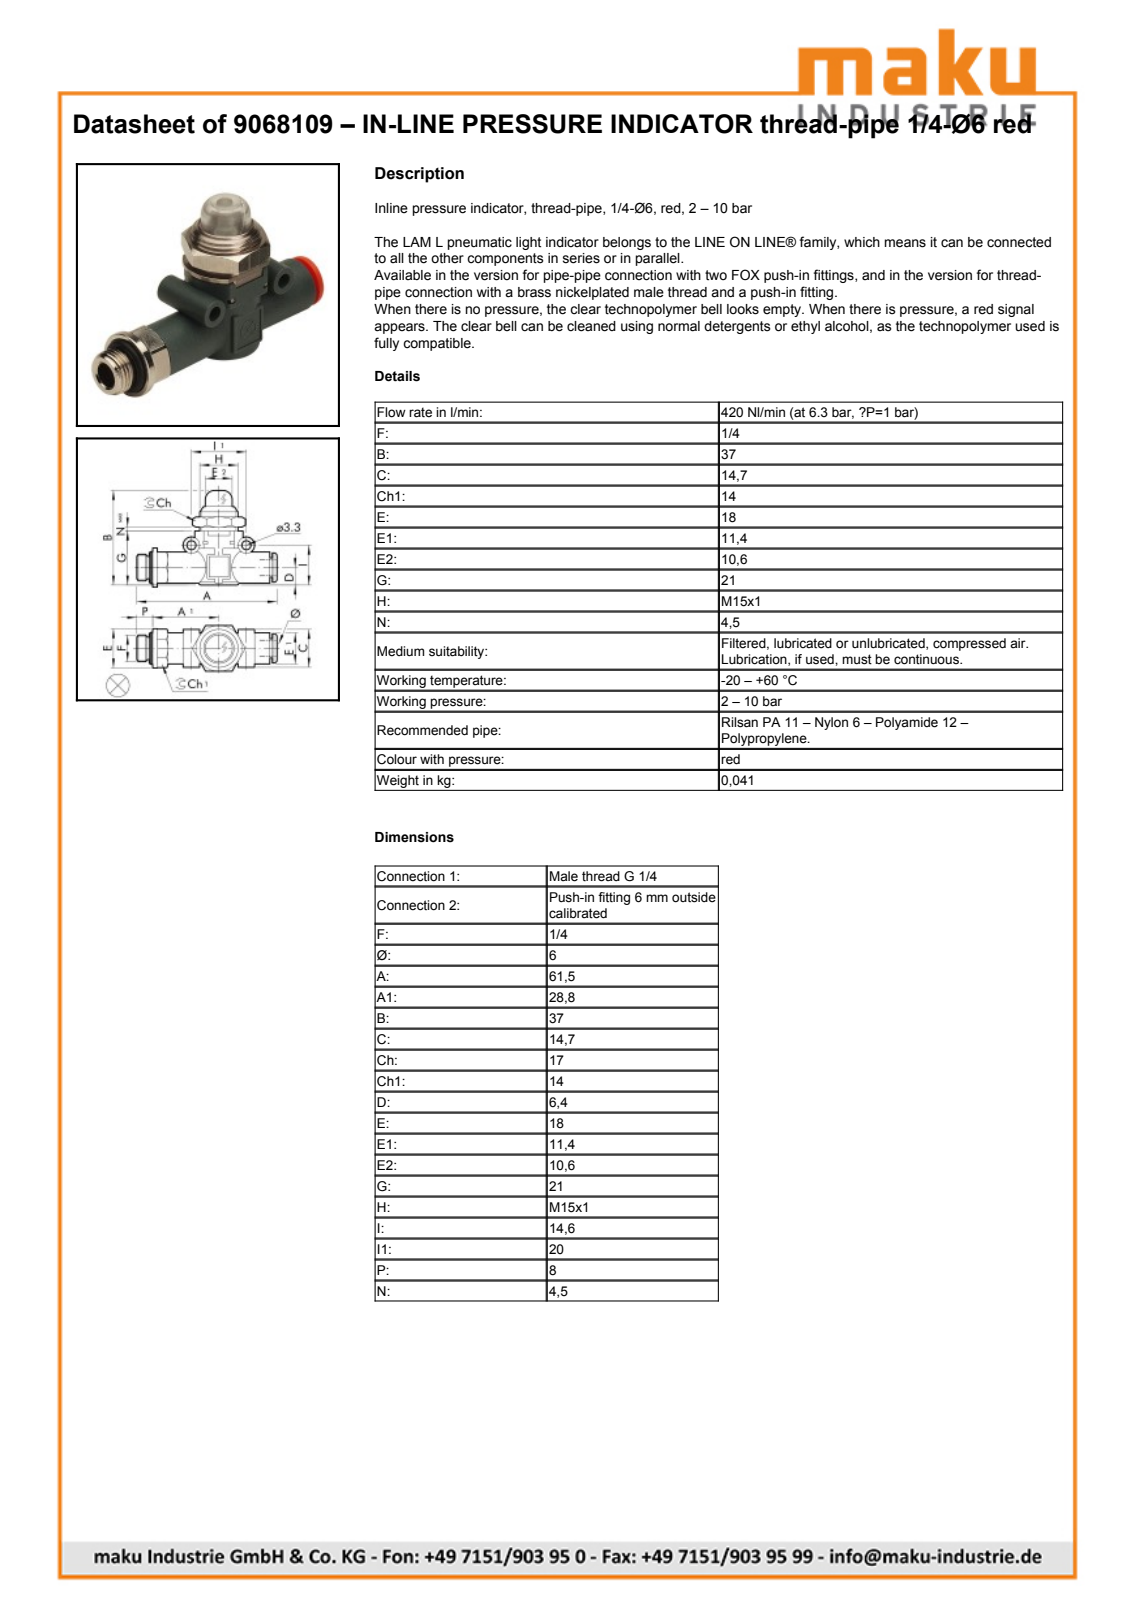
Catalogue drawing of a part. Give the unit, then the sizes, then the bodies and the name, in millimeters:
Units: millimetres
Overall size (bounding box): 61.5 × 39.6 × 18
Round holes (diameter × count): ⌀3.3 ×2, ⌀3.5 ×1, ⌀4 ×1, ⌀6 ×1, ⌀6.2 ×1, ⌀8 ×1, ⌀9 ×1, ⌀9.6 ×1, ⌀10.3 ×1, ⌀11.6 ×1
Round bosses / shafts (diameter × count): ⌀6 ×2, ⌀18 ×1, ⌀14.8 ×1, ⌀14 ×1, ⌀13.16 ×1, ⌀11.4 ×1, ⌀11.1 ×1, ⌀11 ×1
Partial cylindrical surfaces — rounded edges, fillets, slot ends (radius × count): R7.95 ×2, R3.75 ×1, R7.5 ×1, R7.9 ×1, R9.1 ×1, R9.15 ×1, R9.65 ×1
Main face-to-face distances: 14, 17, 14.25, 2.8, 2, 18.4, 12.1, 9.8, 9.3, 16.75
Hole centre spacings: 12.74, 20
Volume: 8 802 mm³ · Surface area: 8 131 mm²
Bodies: 4 solids, 190 faces (97 planar, 63 cylindrical, 30 other)
Part name (STEP PRODUCT): 9068109; LINE-ON-LINE D6 V2v/V3V_L body; LINE-ON-LINE D6 VNR-L bushing; LINE-ON-LINE D6-1/4 thread port (+1 more)
STEP written by: PARTsolutions (AUTOMOTIVE_DESIGN)
